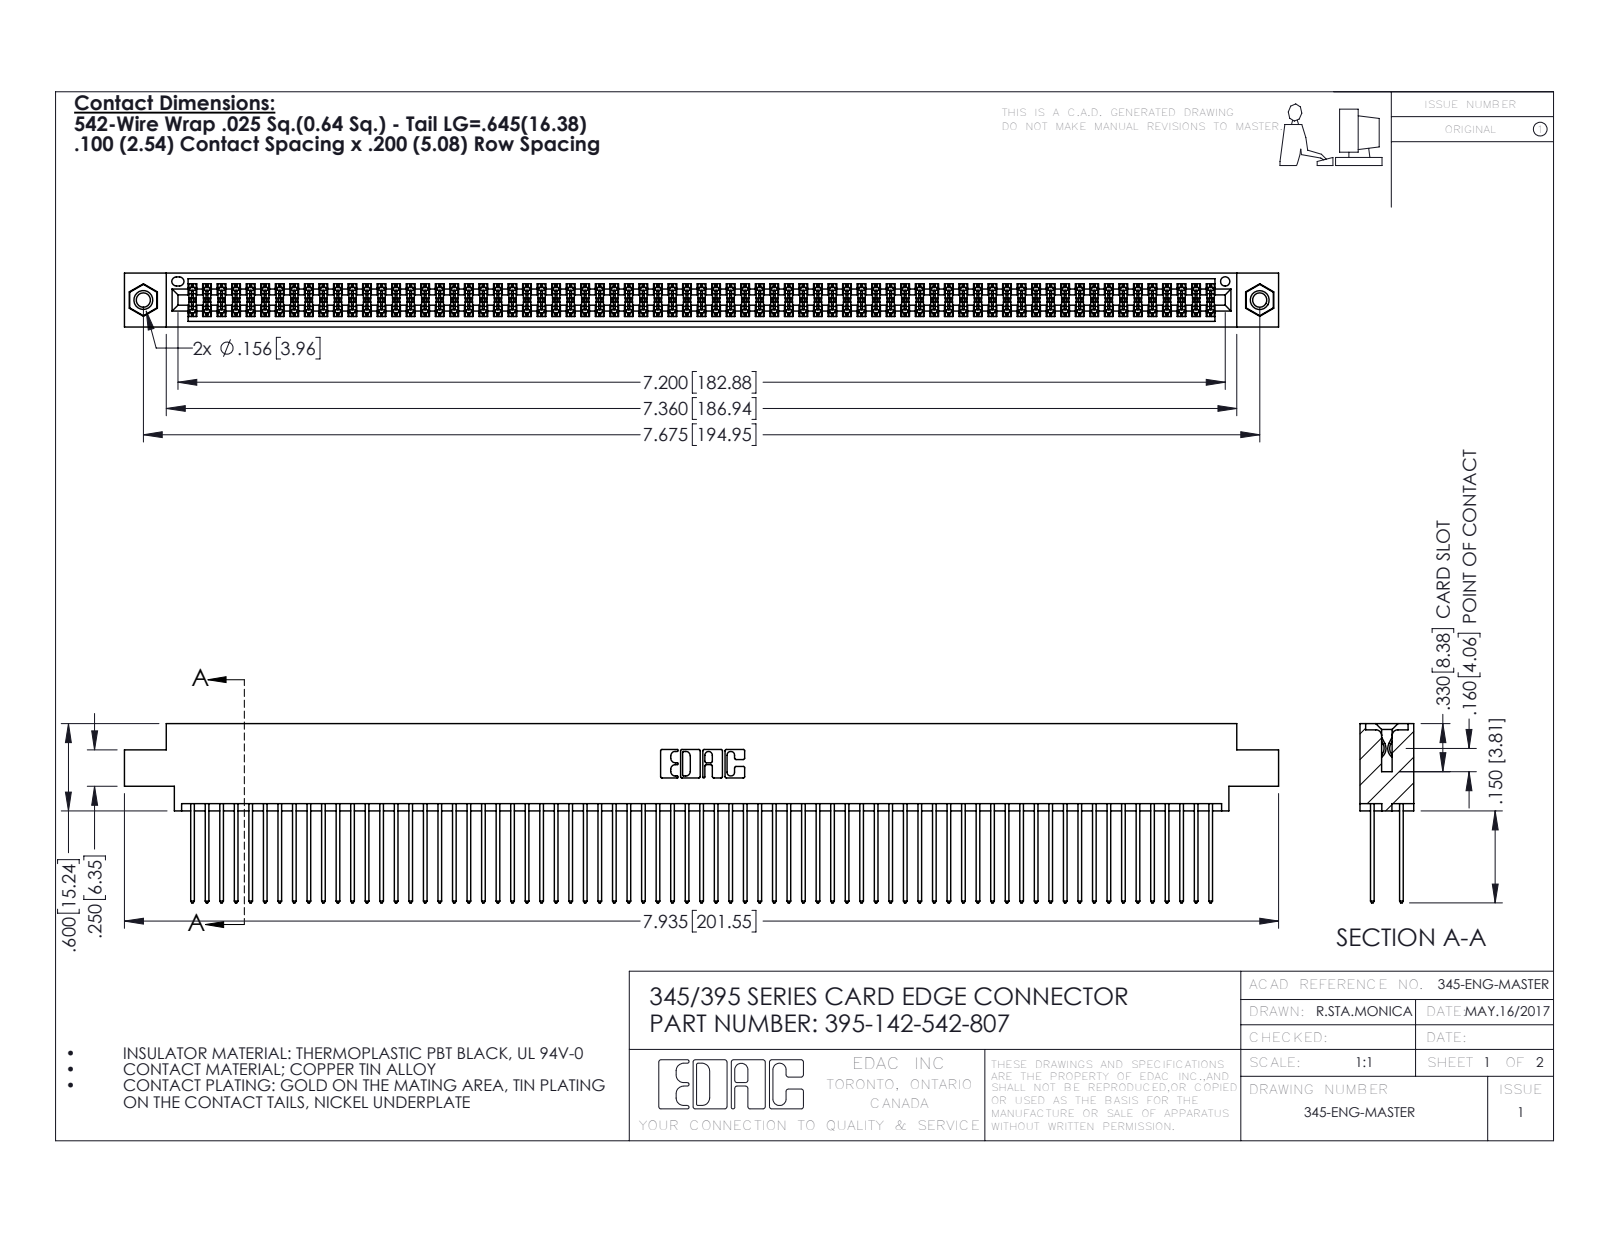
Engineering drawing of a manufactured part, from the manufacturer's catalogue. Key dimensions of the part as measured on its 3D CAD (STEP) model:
Part name (STEP PRODUCT): 345-250-001_345-250-005-103; 395-142-542-807; 345-292-001_345-293-142; 345 Part_0.170 Offset - 0.156 Dia-TI
STEP written by: SolidWorks 2016 (CONFIG_CONTROL_DESIGN)
Units: inches
Bodies: 145 solids, 7290 faces (4802 planar, 2472 cylindrical, 16 other)
Overall size (bounding box): 7.935 × 1.232 × 0.37
Volume: 1.244 in³ · Surface area: 52.63 in²
Round holes (diameter × count): ⌀0.098 ×2, ⌀0.125 ×2, ⌀0.156 ×2, ⌀0.064 ×1
Round bosses / shafts (diameter × count): ⌀0.155 ×2
Partial cylindrical surfaces — rounded edges, fillets, slot ends (radius × count): R0.006 ×213, R0.01 ×142, R0.01 ×22, R0.007 ×6, R0.031 ×6, R0.026 ×3, R0.014 ×2, R0.019 ×2
Main face-to-face distances: 0.072, 0.298, 0.2, 0.098, 0.272, 0.025, 0.225, 0.37, 0.175, 0.149
Hole centre spacings: 0.27, 7.439, 7.675
